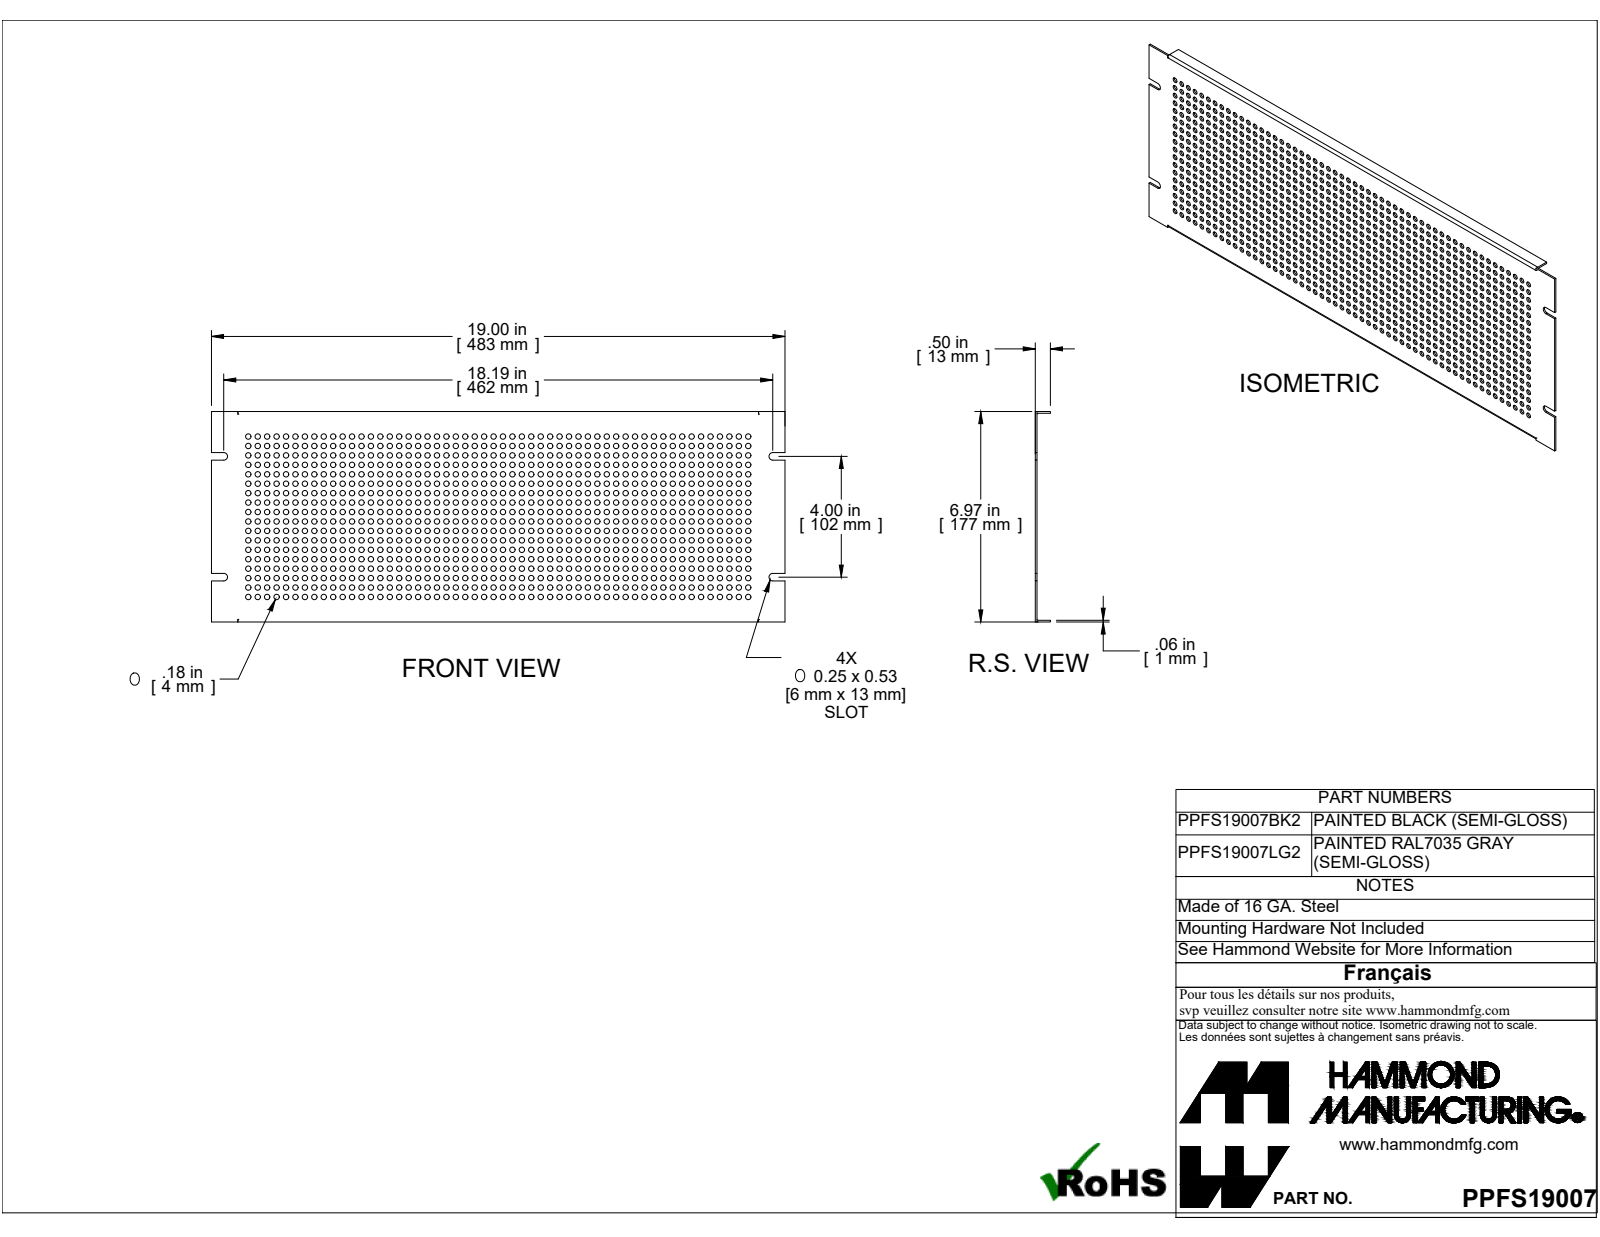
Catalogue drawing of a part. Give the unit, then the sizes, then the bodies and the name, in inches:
Units: inches
Overall size (bounding box): 19 × 6.968 × 0.5
Round holes (diameter × count): ⌀0.177 ×972
Partial cylindrical surfaces — rounded edges, fillets, slot ends (radius × count): R0.125 ×4, R0.029 ×2, R0.086 ×2
Main face-to-face distances: 0.057, 0.057, 6.911, 6.968, 6.854, 0.5, 0.443, 19, 0.875, 18.125
Hole centre spacings: 1.25, 0.313, 1.289, 0.312, 0.937, 0.442, 0.988, 1.563
Volume: 6.977 in³ · Surface area: 278.9 in²
Bodies: 1 solid, 1018 faces (38 planar, 980 cylindrical, 0 other)
Part name (STEP PRODUCT): PPFS19007LG2
STEP written by: SolidWorks 2019 (CONFIG_CONTROL_DESIGN)
